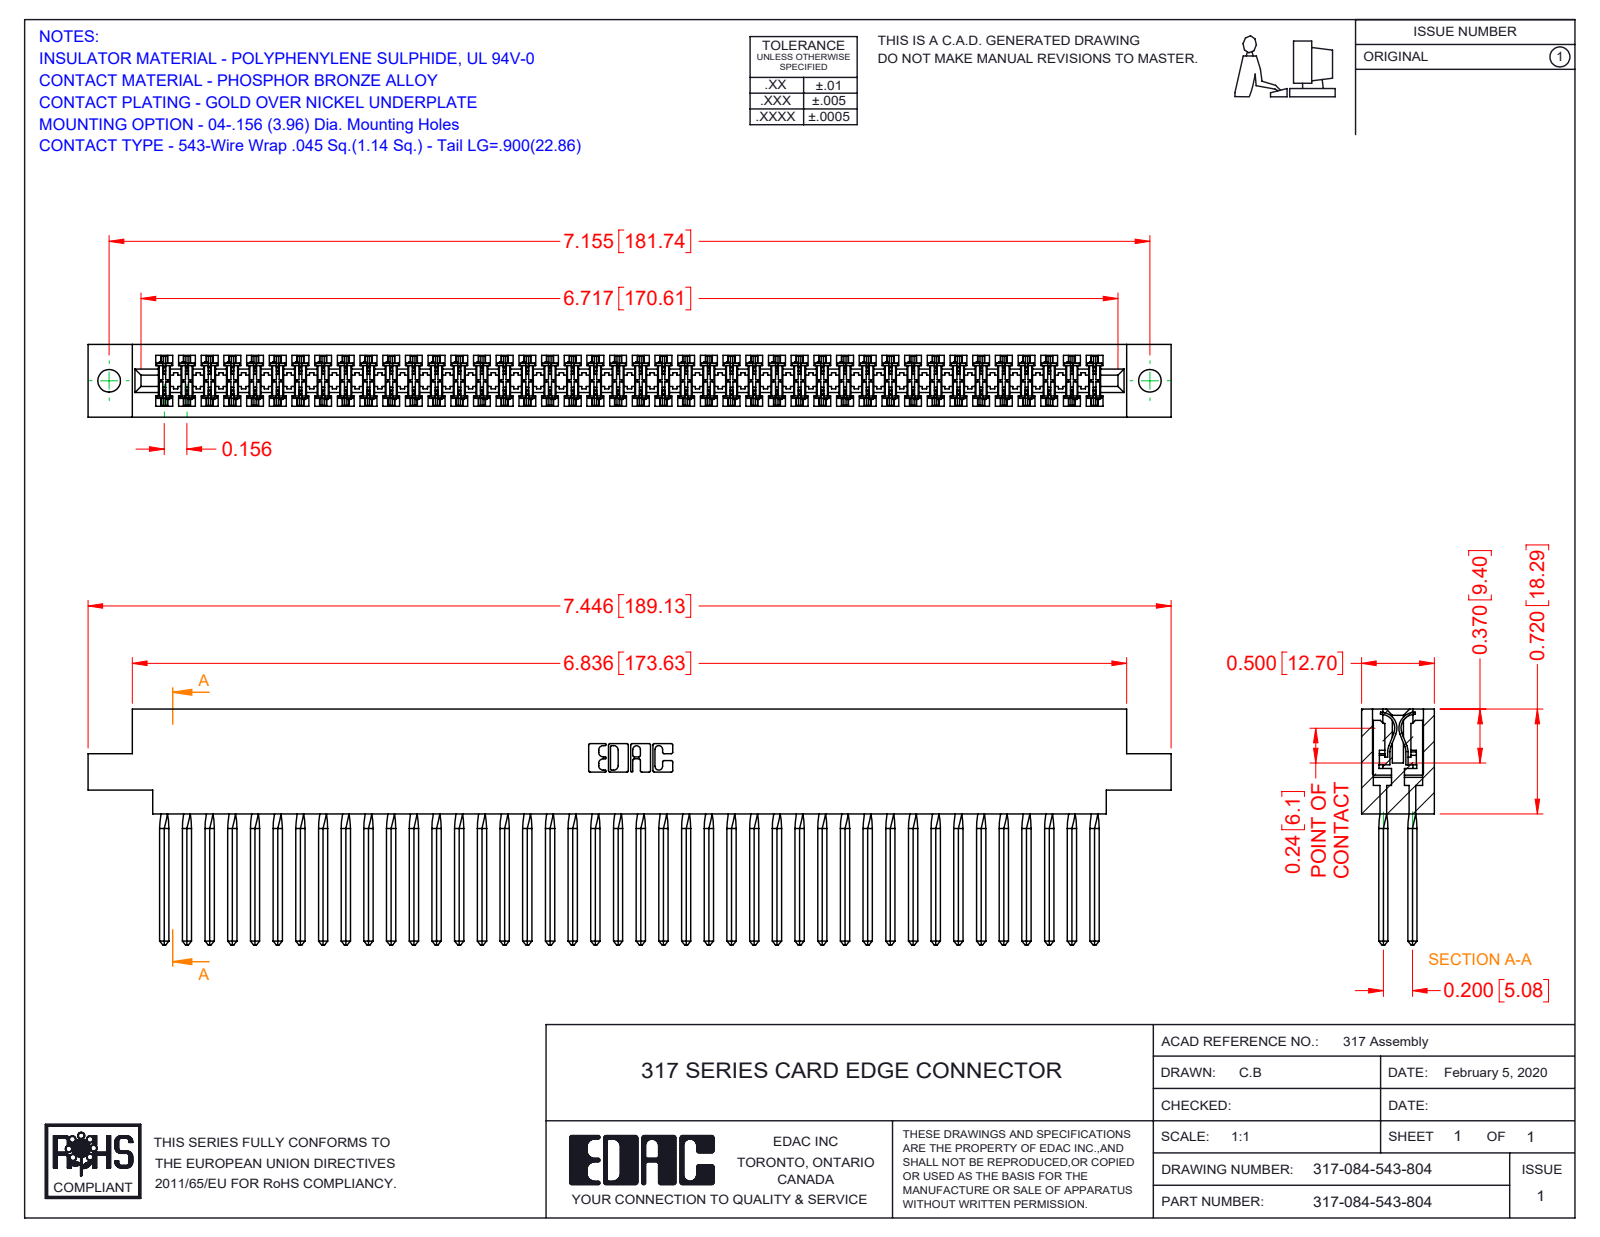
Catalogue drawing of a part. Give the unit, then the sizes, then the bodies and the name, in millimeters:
Units: millimetres
Overall size (bounding box): 189.1 × 41.1 × 12.7
Round holes (diameter × count): ⌀4 ×2
Partial cylindrical surfaces — rounded edges, fillets, slot ends (radius × count): R0.4 ×168, R0.3 ×22, R0.2 ×6, R0.8 ×6, R0.7 ×3, R2.4 ×2, R2.5 ×2, R2.8 ×2
Main face-to-face distances: 12.7, 1.9, 10.8, 8.9, 5, 2.8, 2.4, 5.1, 2.9, 3.3
Hole centre spacings: 181.7
Volume: 32 070 mm³ · Surface area: 48 480 mm²
Bodies: 85 solids, 7578 faces (6190 planar, 1052 cylindrical, 336 other)
Part name (STEP PRODUCT): 317-290-001_543; 317-084-543-804; 317 Part_.156 Dia - TH
STEP written by: SolidWorks 2016 (CONFIG_CONTROL_DESIGN)
